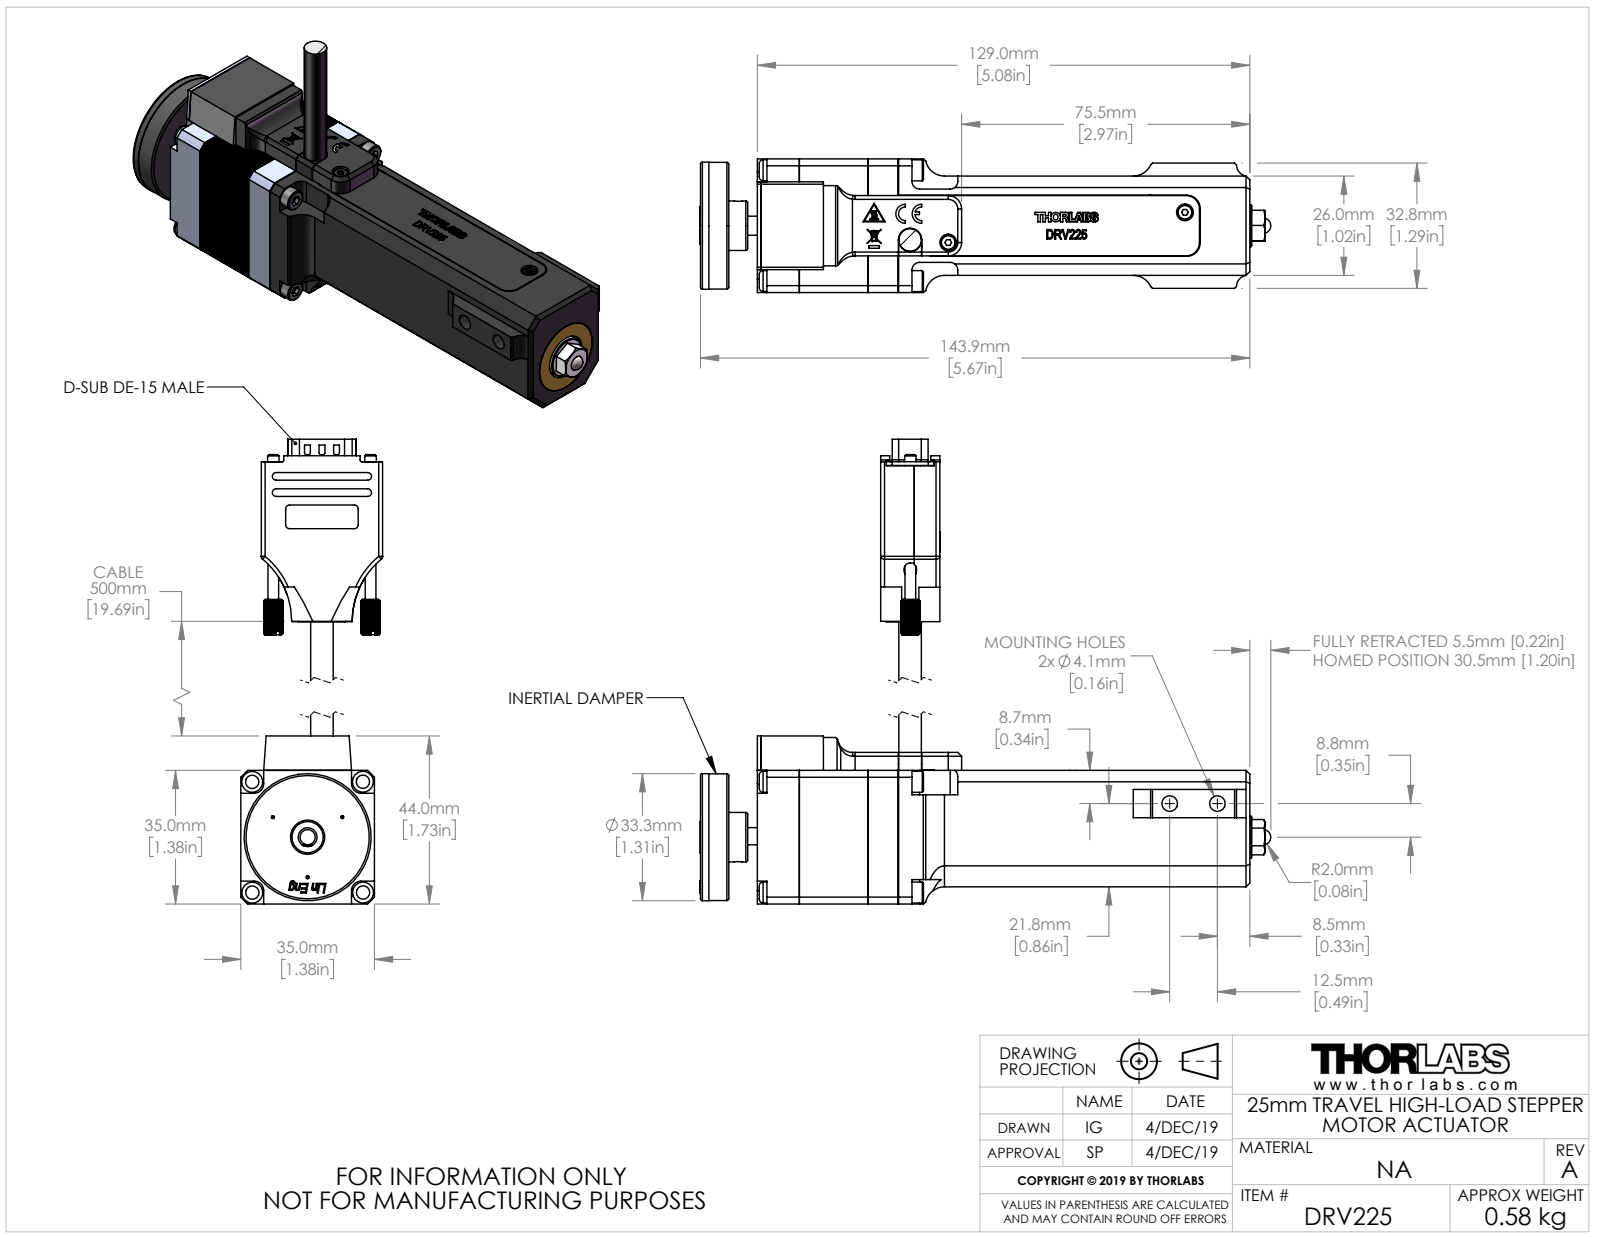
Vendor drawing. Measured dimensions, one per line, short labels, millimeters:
name: DRV225 - 25mm Trapezoidal Stepper Motor Drive
written by: SolidWorks 2019 (AUTOMOTIVE_DESIGN)
unit: mm
bodies: 22 solids, 1014 faces (587 planar, 0 cylindrical, 427 other)
size: 149.6 × 77.46 × 35
volume: 120 173 mm³; area: 53 961 mm²
face distances: 4.5, 30.5, 26, 35, 18, 29, 8, 1.5, 37, 6
